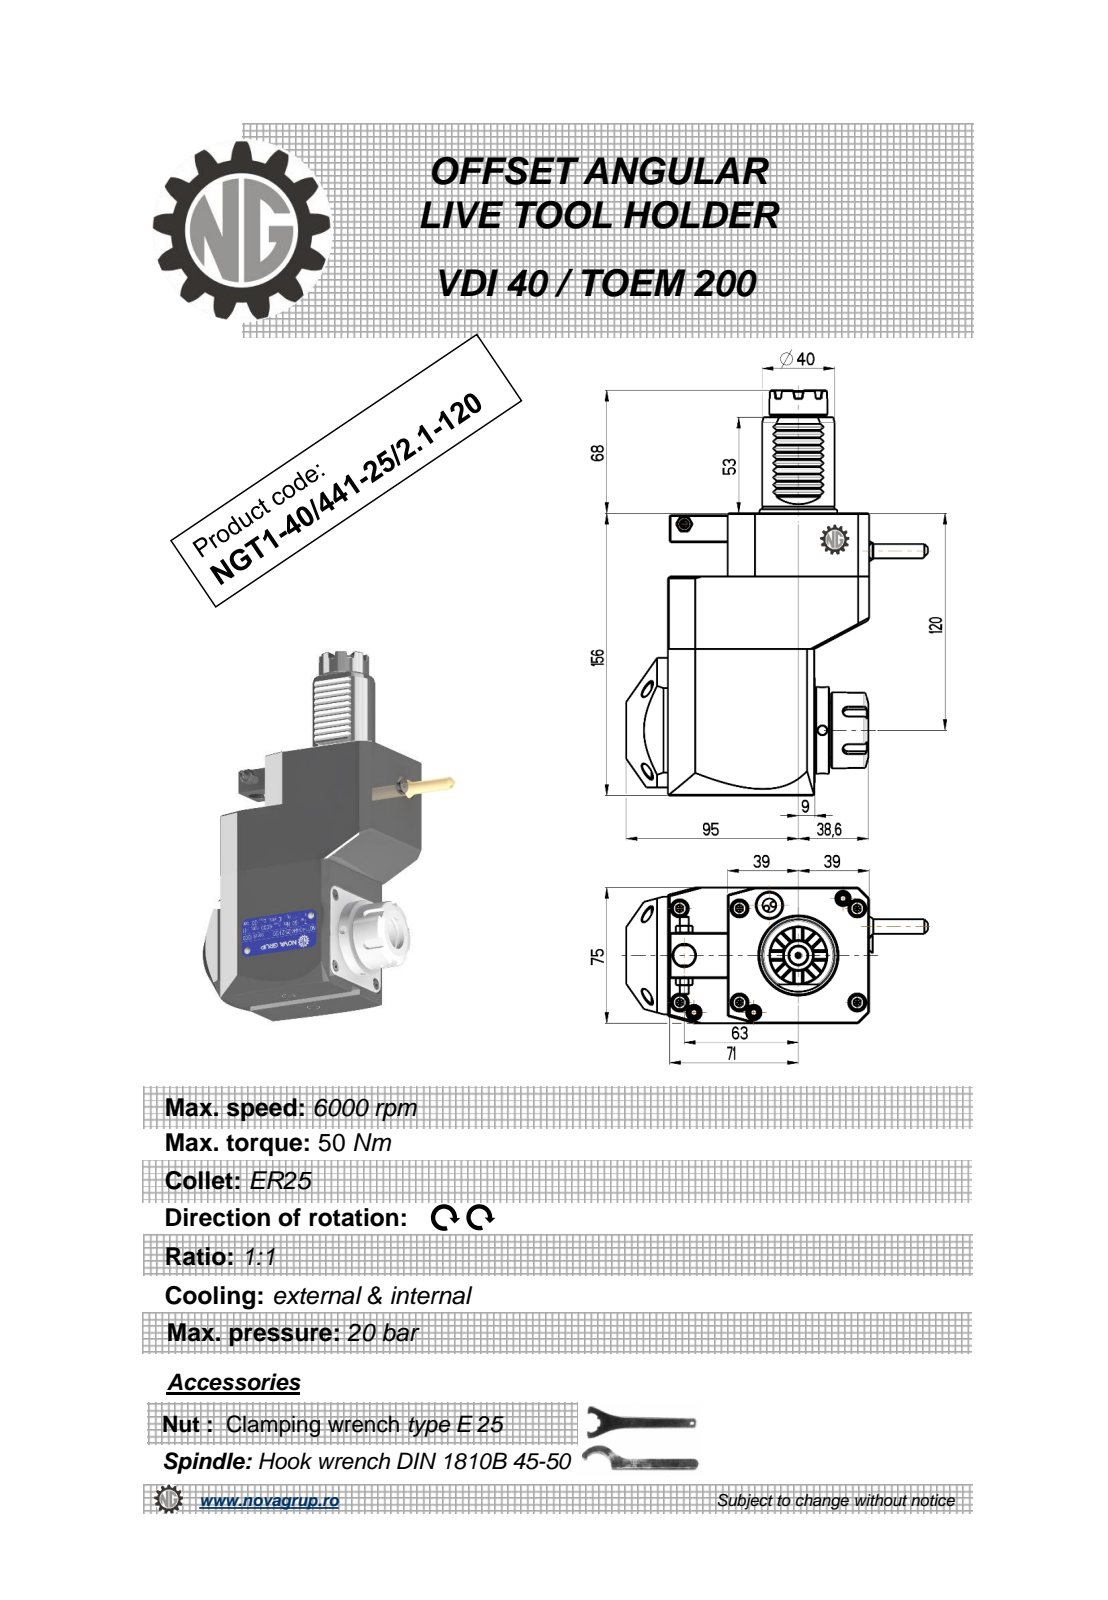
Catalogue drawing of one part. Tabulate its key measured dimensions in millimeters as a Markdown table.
| quantity | value |
| --- | --- |
| part name | NGT1_40_441_25_2_1_120 |
| STEP written by | PRO/ENGINEER BY PARAMETRIC TECHNOLOGY CORPORATION, 2010280 (CONFIG_CONTROL_DESIGN) |
| units | millimeters |
| bodies | 1 solid, 523 faces (240 planar, 94 cylindrical, 189 other) |
| overall size | 224 × 166.5 × 76.6 |
| volume | 1 185 000 mm³ |
| surface area | 88 880 mm² |
| round holes (diameter × count) | 5 × 3, 3 × 1, 9.5 × 1, 12 × 1, 20.3 × 1 |
| round bosses / shafts (diameter × count) | 48 × 1, 42 × 1, 40 × 1, 37.5 × 1, 33 × 1, 32 × 1, 17 × 1, 10 × 1 |
| partial cylindrical surfaces (radius × count) | 0.26 × 12, 0.3 × 10, 0.2 × 6, 3 × 5, 0.5 × 1, 8.6 × 1, 40 × 1 |
| main face-to-face distances | 75, 156, 111, 35, 121, 81, 30, 33, 78, 48 |
| hole center spacings | 20.93, 76.25, 100.28, 112.5 |
